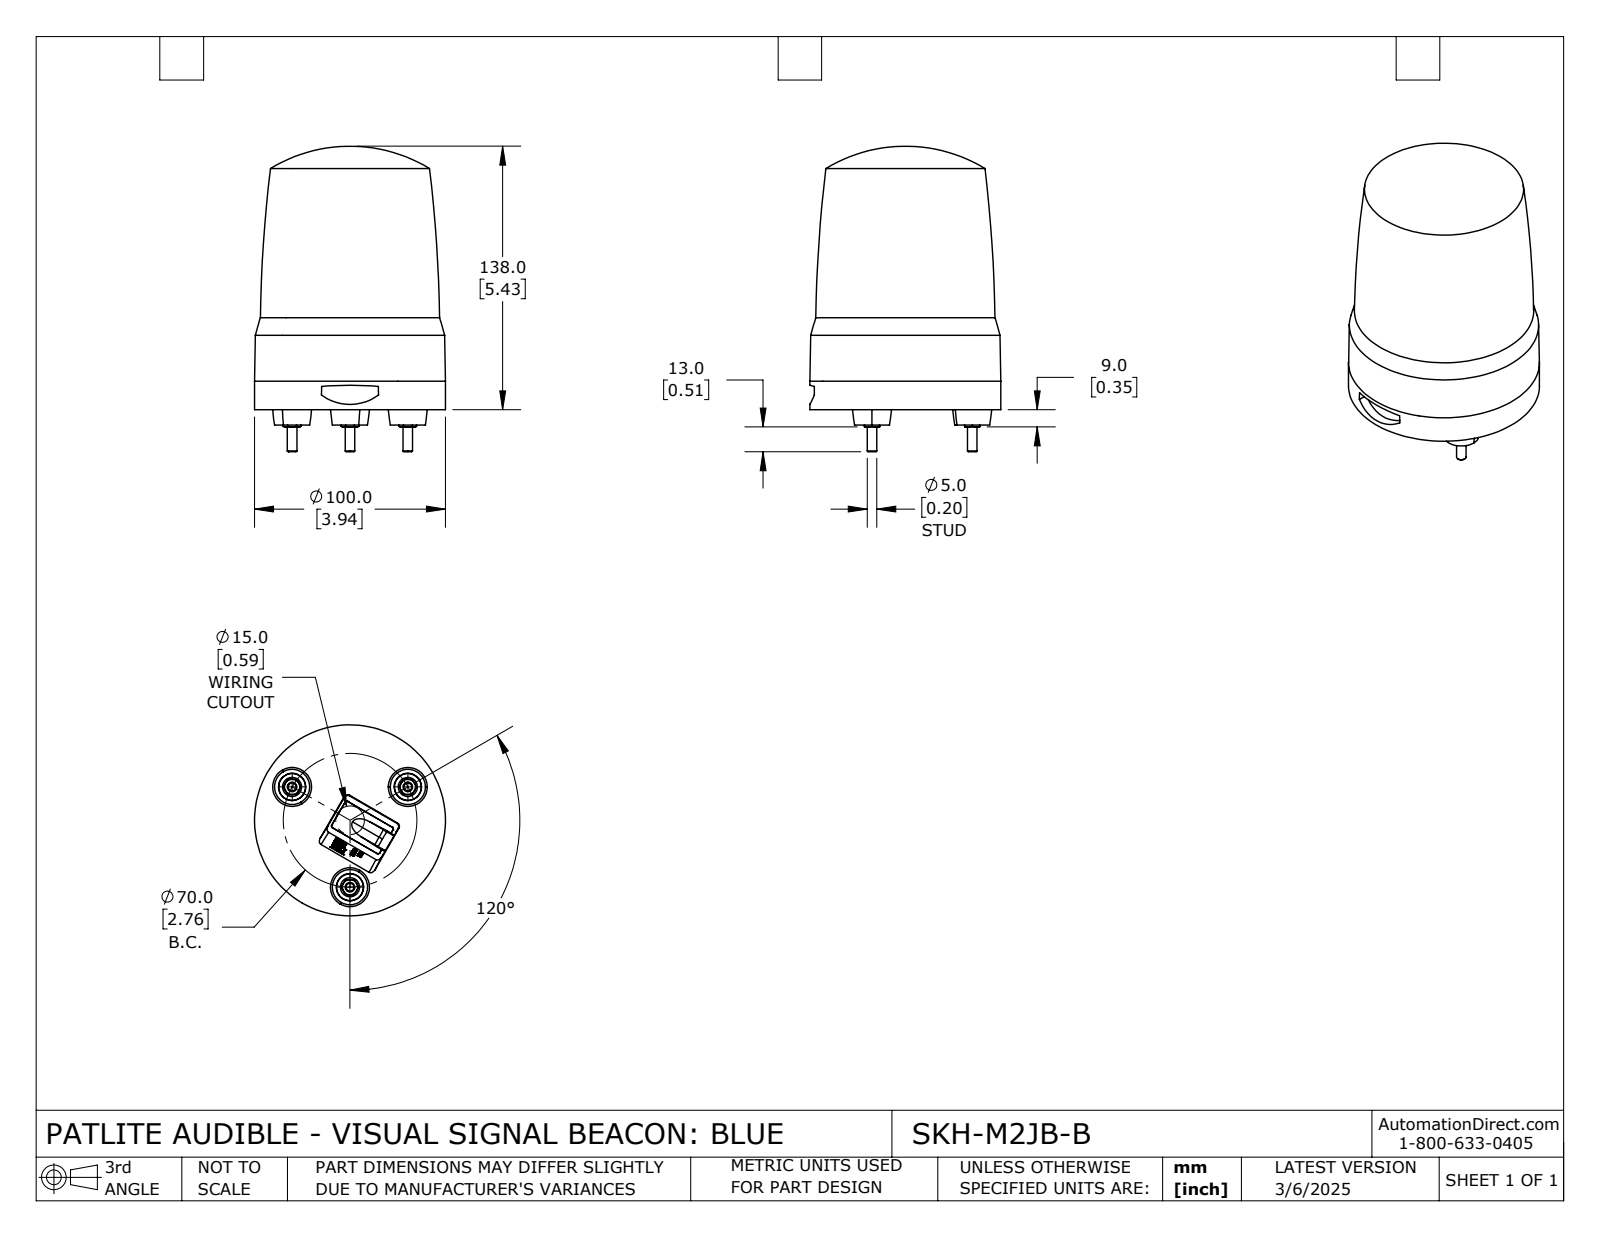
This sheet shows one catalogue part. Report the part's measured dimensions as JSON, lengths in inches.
{"part_name": "SKH-M2JB-B", "step_written_by": "SolidWorks 2024 (CONFIG_CONTROL_DESIGN)", "units": "inches", "bodies": {"solids": 1, "faces": 446, "planar": 211, "cylindrical": 22, "other": 213}, "overall_size": [6.299, 3.937, 3.937], "volume_in3": 54.94, "surface_area_in2": 85.92, "round_bosses_or_shafts": [[0.394, 3], [0.197, 3], [3.937, 1]], "partial_cylinders_radius": [[0.079, 4], [0.199, 2], [1.772, 1], [3.154, 1]], "face_to_face_distances": [0.315, 0.585, 0.27, 0.063, 0.648, 0.333, 0.15, 0.165, 0.435, 0.498]}
